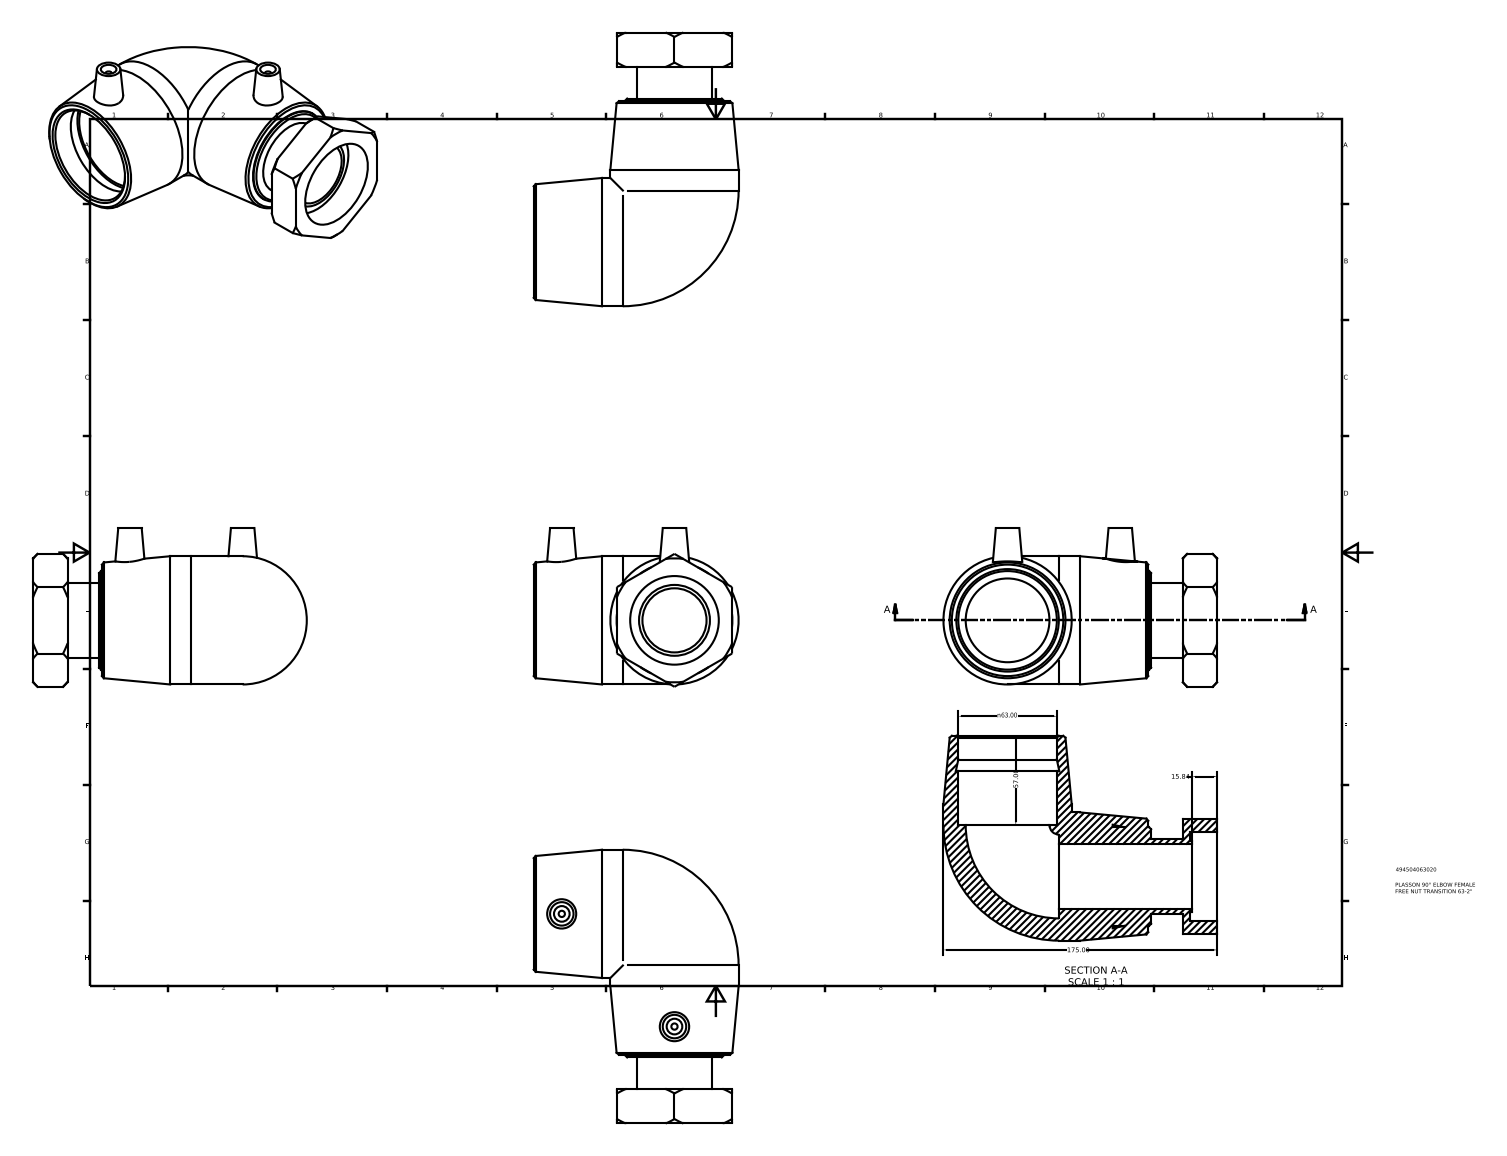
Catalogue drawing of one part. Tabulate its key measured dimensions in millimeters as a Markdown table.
| quantity | value |
| --- | --- |
| part name | 494504063020 |
| STEP written by | Autodesk Inventor 2015 (AUTOMOTIVE_DESIGN) |
| units | millimeters |
| bodies | 1 solid, 61 faces (23 planar, 14 cylindrical, 24 other) |
| overall size | 175 × 131 × 101.49 |
| volume | 535 900 mm³ |
| surface area | 102 882 mm² |
| round holes (diameter × count) | 10 × 2, 41 × 1, 56.66 × 1, 63 × 1 |
| round bosses / shafts (diameter × count) | 82 × 2, 4 × 2, 63 × 1, 48.16 × 1, 45.32 × 1 |
| main face-to-face distances | 22, 73.6, 57, 1.76, 26.4, 20.24, 42.24, 58.76, 79, 101 |
| hole center spacings | 101.89 |
